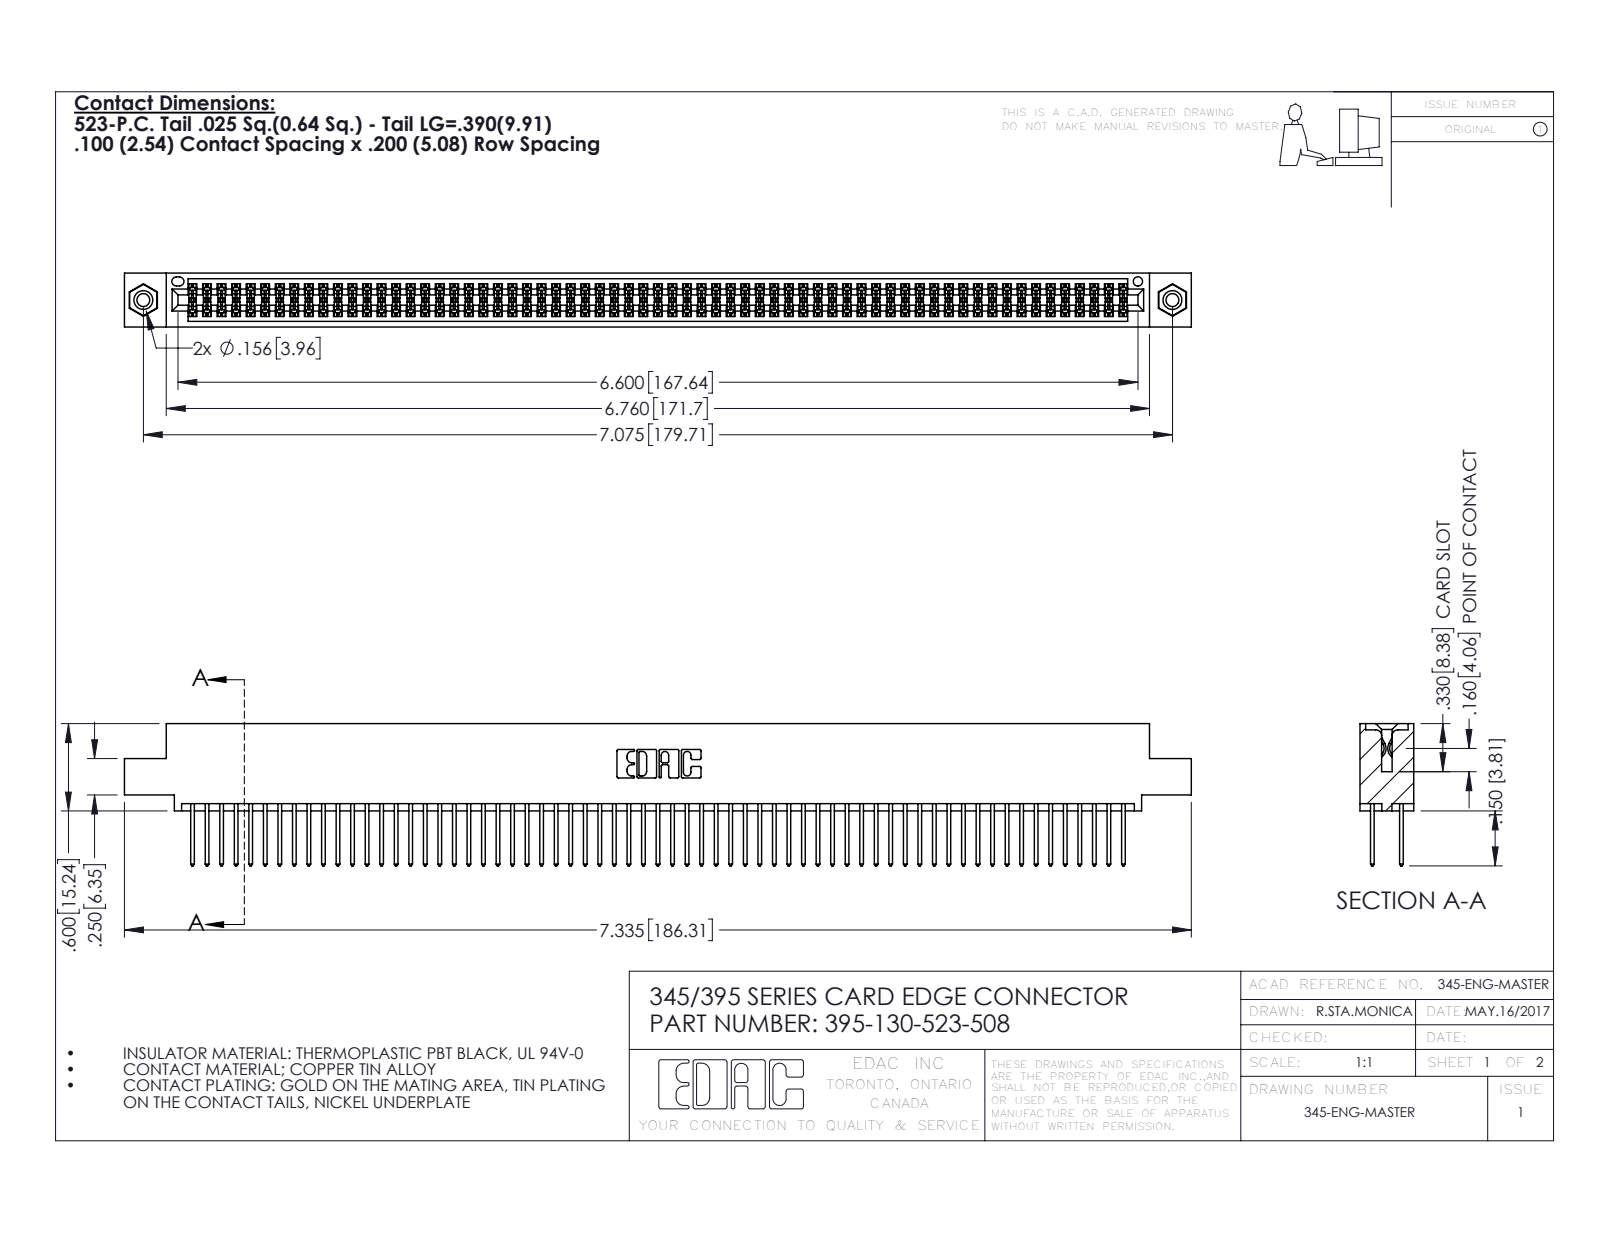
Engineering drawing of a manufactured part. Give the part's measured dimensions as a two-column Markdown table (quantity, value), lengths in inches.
| quantity | value |
| --- | --- |
| part name | 395-130-523-508; 345 Part_0.110 Offset - 0.156 Dia-TI; 345-250-001_345-250-003-102; 345-292-001_345-293-123 |
| STEP written by | SolidWorks 2016 (CONFIG_CONTROL_DESIGN) |
| units | inches |
| bodies | 133 solids, 6690 faces (4406 planar, 2268 cylindrical, 16 other) |
| overall size | 7.335 × 0.977 × 0.37 |
| volume | 1.129 in³ |
| surface area | 45.09 in² |
| round holes (diameter × count) | 0.089 × 2, 0.125 × 2, 0.156 × 2, 0.064 × 1 |
| round bosses / shafts (diameter × count) | 0.155 × 2 |
| partial cylindrical surfaces (radius × count) | 0.006 × 195, 0.01 × 130, 0.01 × 22, 0.007 × 6, 0.031 × 6, 0.026 × 3, 0.014 × 2, 0.019 × 2 |
| main face-to-face distances | 0.072, 0.298, 0.2, 0.098, 0.272, 0.025, 0.37, 0.225, 0.175, 0.149 |
| hole center spacings | 0.27, 6.839, 7.075 |
